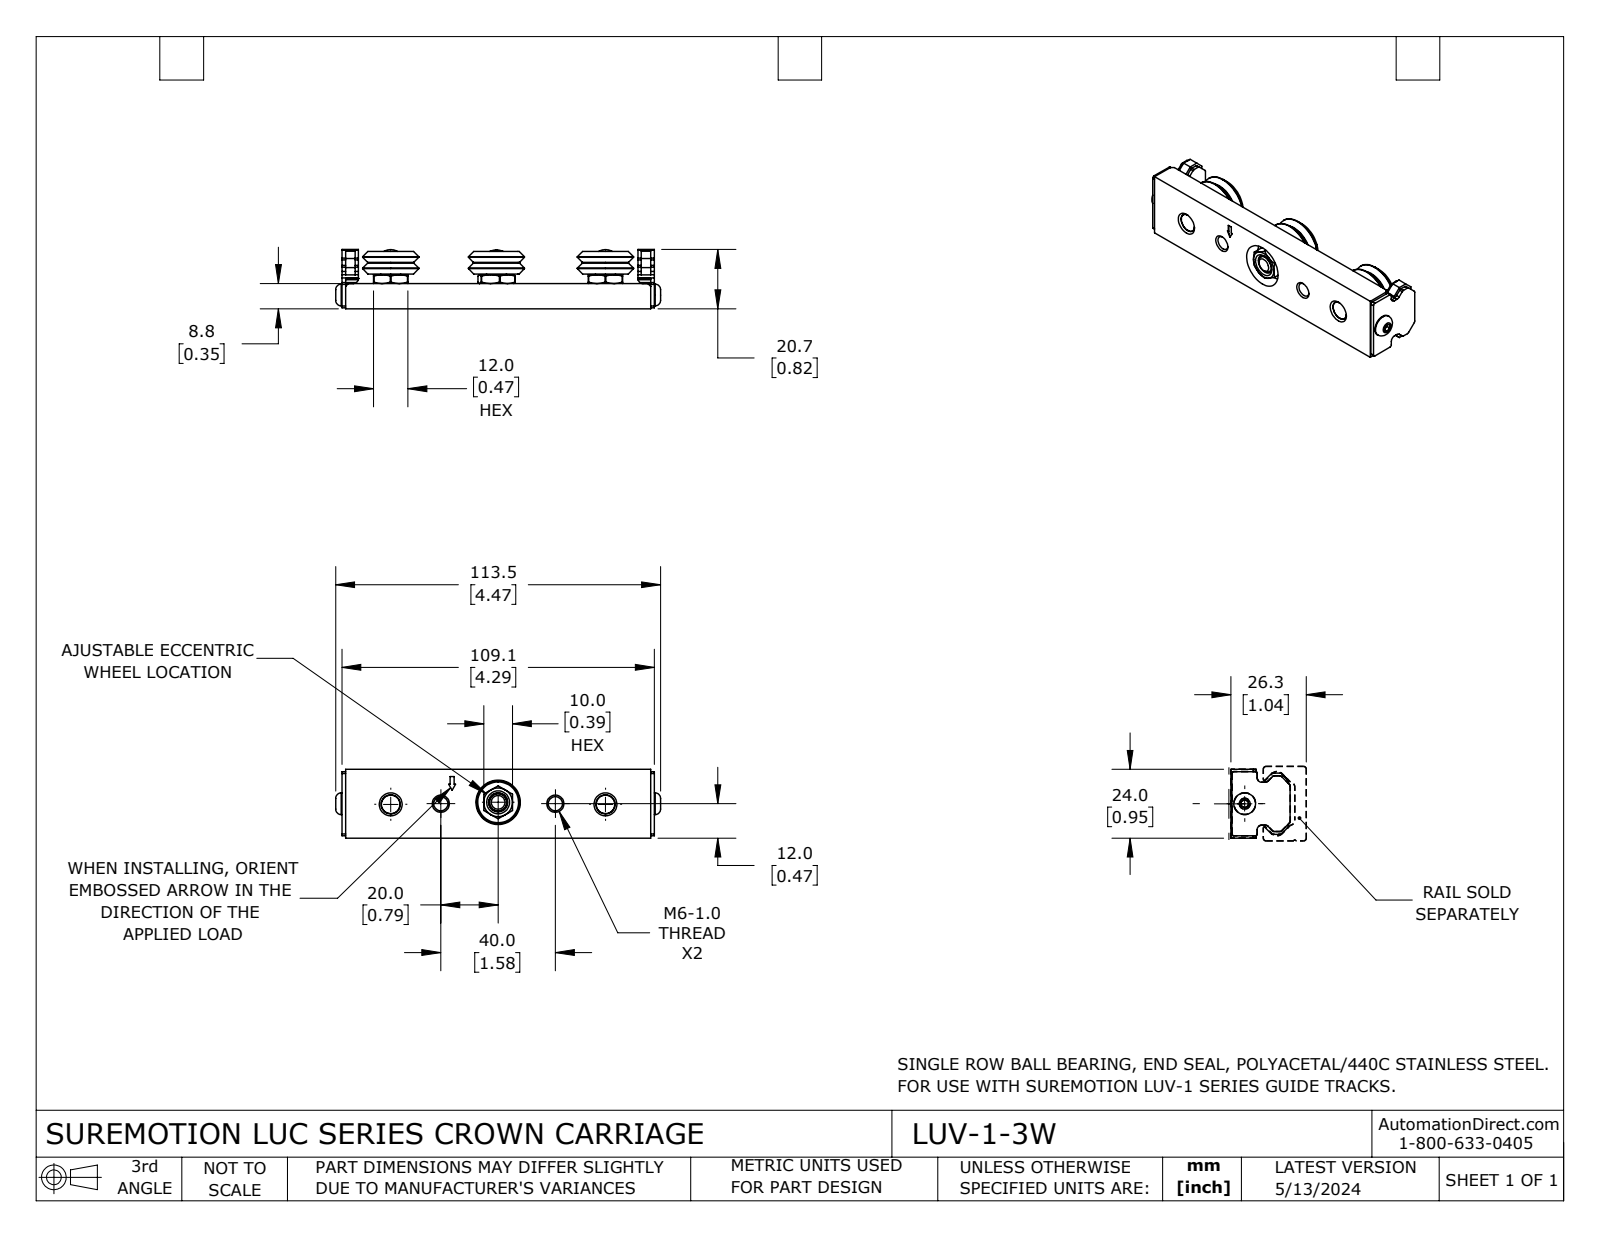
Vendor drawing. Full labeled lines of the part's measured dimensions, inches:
Part name (STEP PRODUCT): LUV-1-3W
STEP written by: SolidWorks 2023 (CONFIG_CONTROL_DESIGN)
Units: inches
Bodies: 7 solids, 651 faces (212 planar, 196 cylindrical, 243 other)
Overall size (bounding box): 4.467 × 0.945 × 0.816
Volume: 1.923 in³ · Surface area: 25.89 in²
Round holes (diameter × count): ⌀0.187 ×3, ⌀0.262 ×3, ⌀0.48 ×3, ⌀0.489 ×3, ⌀0.128 ×1, ⌀0.194 ×1, ⌀0.194 ×1, ⌀0.25 ×1, ⌀0.61 ×1
Round bosses / shafts (diameter × count): ⌀0.771 ×3, ⌀0.333 ×3, ⌀0.324 ×3, ⌀0.187 ×3, ⌀0.315 ×2, ⌀0.236 ×2, ⌀0.561 ×1, ⌀0.299 ×1
Partial cylindrical surfaces — rounded edges, fillets, slot ends (radius × count): R0.015 ×12, R0.033 ×6, R0.025 ×4, R0.063 ×4, R0.269 ×3, R0.07 ×2
Main face-to-face distances: 0.347, 0.945, 0.05, 4.244, 4.194, 0.301, 4.294, 0.225, 4.069, 0.175
Hole centre spacings: 0.689, 2.264, 0.024, 0.766, 0.787, 0.789, 0.809, 1.455
